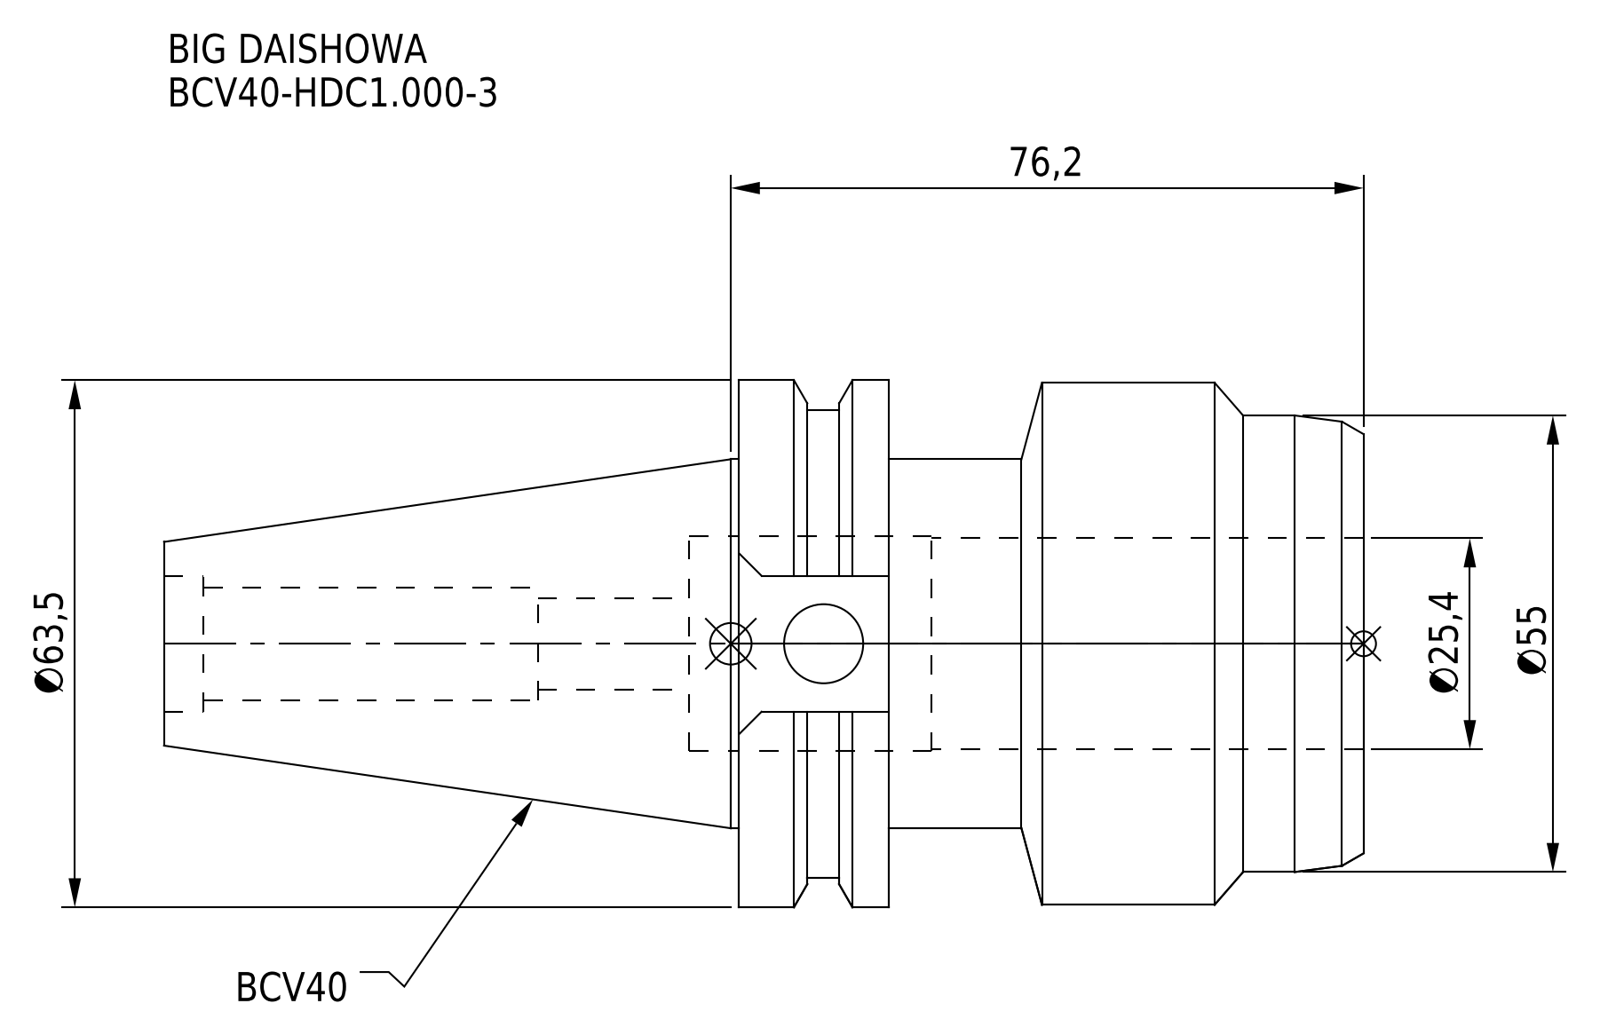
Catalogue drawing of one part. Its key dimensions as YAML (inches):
part_name: "BCV40-HDC1_000-3"
step_written_by: "CREO PARAMETRIC BY PTC INC, 2016380 (AUTOMOTIVE_DESIGN)"
units: inches
bodies: {solids: 1, faces: 65, planar: 23, cylindrical: 28, other: 14}
overall_size: [5.687, 2.5, 2.476]
volume: 12.47
surface_area: 58.67
round_holes:
  - {diameter: 0.375, count: 1}
  - {diameter: 0.433, count: 1}
  - {diameter: 0.535, count: 1}
  - {diameter: 0.643, count: 1}
  - {diameter: 1, count: 1}
  - {diameter: 1.02, count: 1}
round_bosses_or_shafts:
  - {diameter: 2.5, count: 1}
  - {diameter: 2.476, count: 1}
  - {diameter: 2.219, count: 1}
  - {diameter: 2.165, count: 1}
  - {diameter: 1.75, count: 1}
face_to_face_distances: [0.711, 2.25, 2.961, 0.236, 3.197, 0.947, 5.687, 3.437, 2.726, 2.49]
